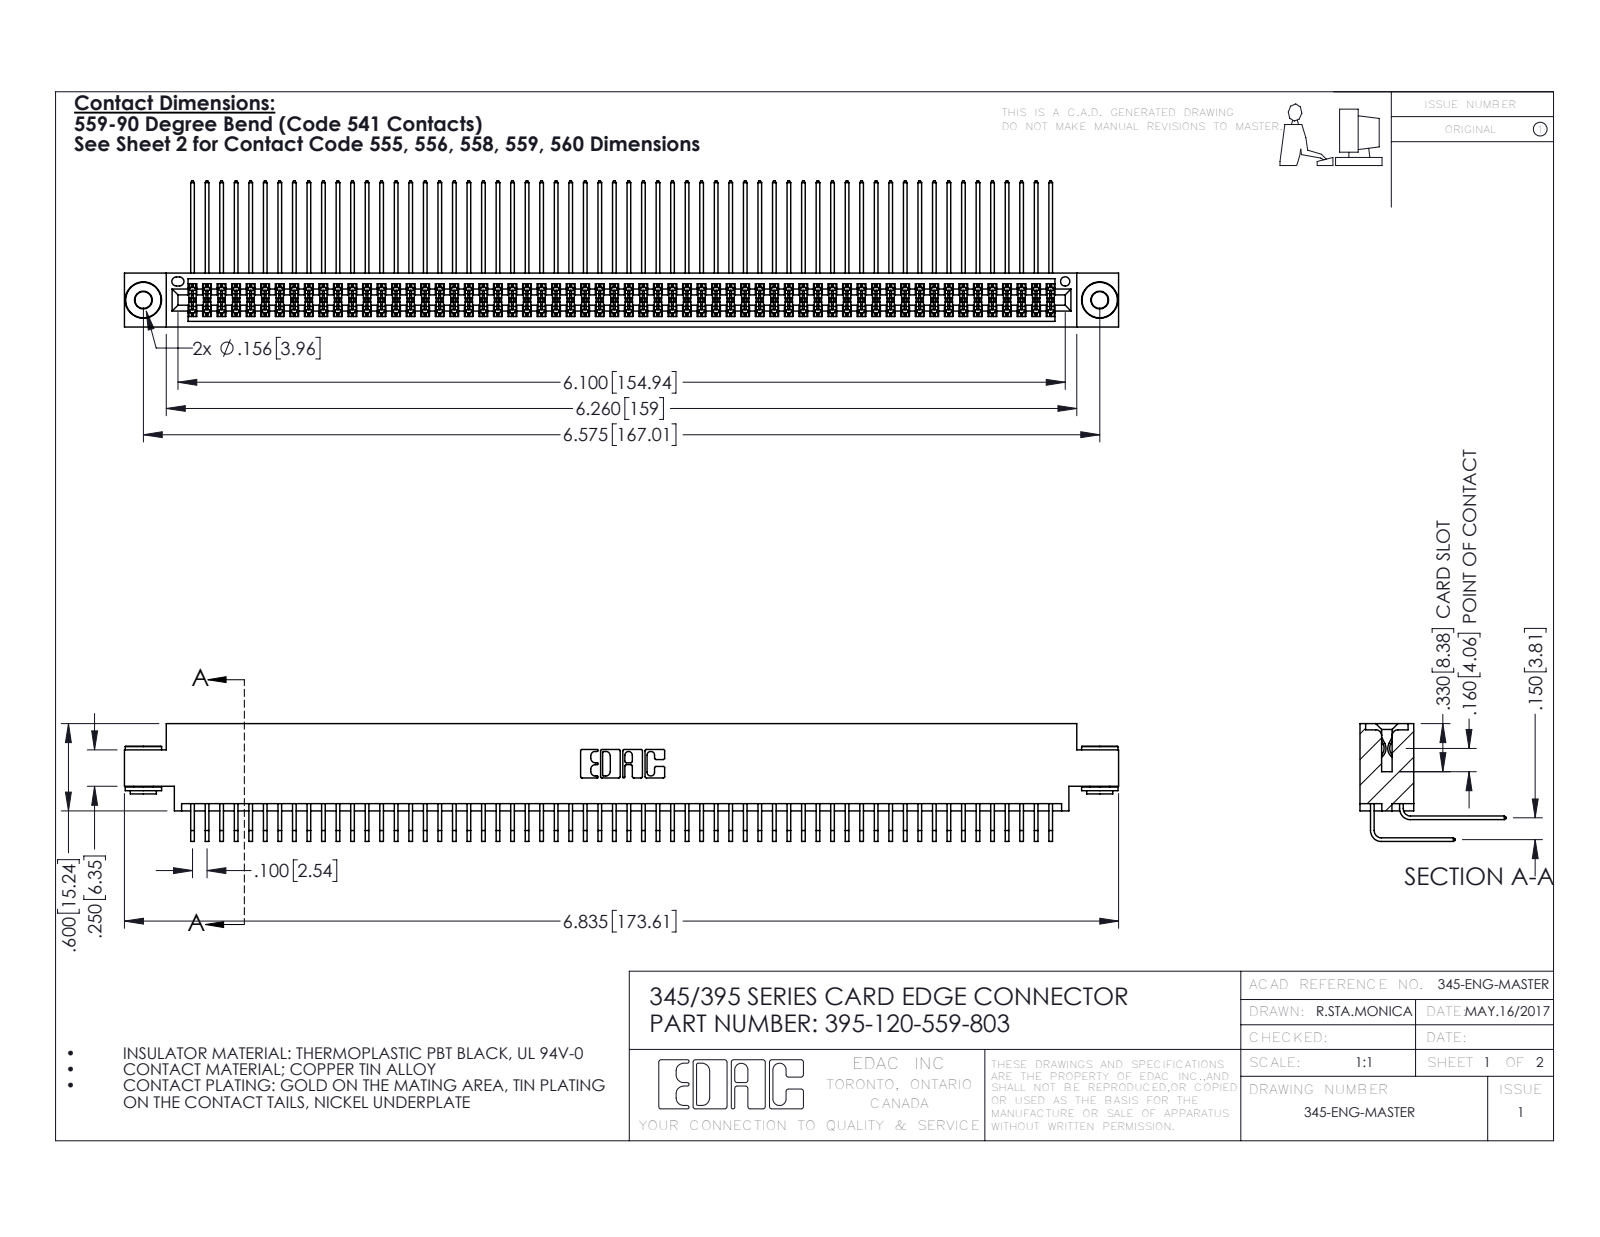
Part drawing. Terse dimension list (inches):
name: 345 Part_0.170 Offset - 0.156 Dia-TH; 345-292-001_559 Tail - 2; 345-292-001_558 559 Tail - 1; 395-120-559-803 (+1 more)
written by: SolidWorks 2016 (CONFIG_CONTROL_DESIGN)
unit: in
bodies: 123 solids, 6408 faces (4294 planar, 2106 cylindrical, 8 other)
size: 6.835 × 1.005 × 0.809
volume: 1.076 in³; area: 46.52 in²
holes: 2× ⌀0.116, 2× ⌀0.156, 1× ⌀0.064
bosses: 2× ⌀0.25, 2× ⌀0.18, 2× ⌀0.136
rounds: 180× R0.006, 22× R0.01, 6× R0.007, 6× R0.031, 3× R0.026, 2× R0.014, 2× R0.019, 2× R0.022
face distances: 0.072, 0.298, 0.37, 0.2, 0.098, 0.272, 0.025, 0.225, 0.175, 0.15
hole spacings: 0.27, 6.339, 6.575
